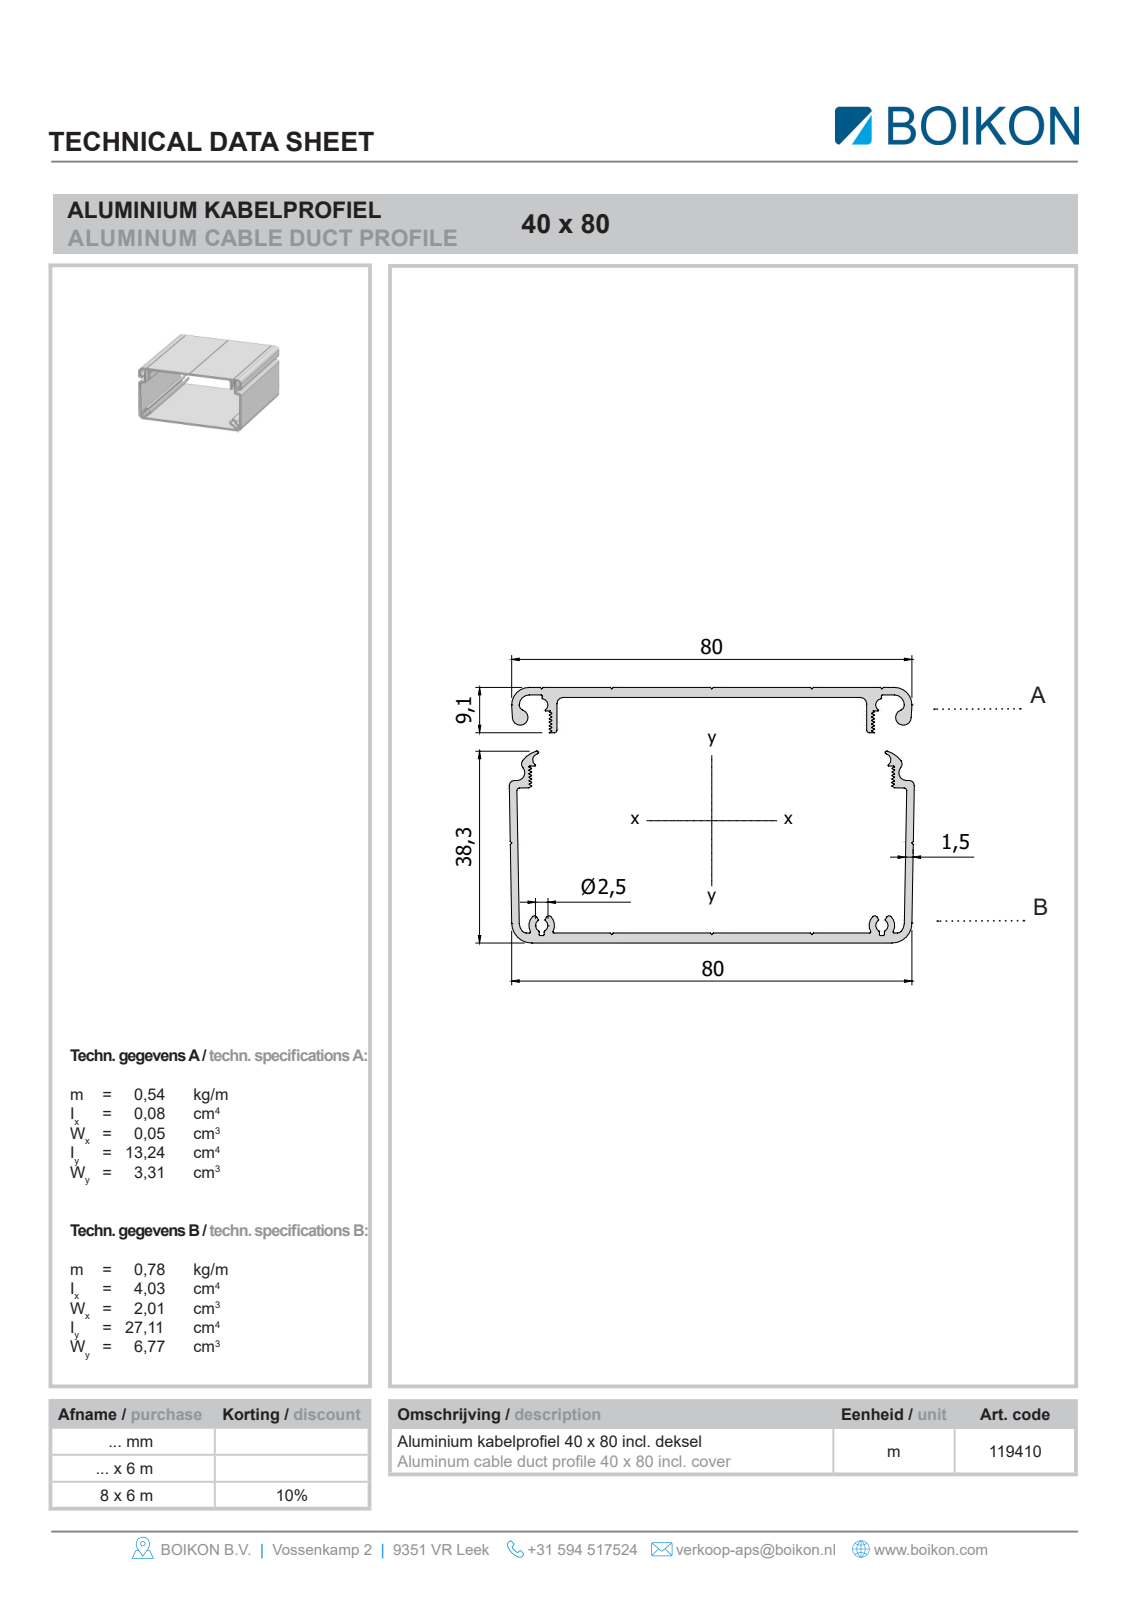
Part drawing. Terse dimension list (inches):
name: Root; 119410Kabelgootprofiel 40x80BOIKON0
written by: HiCAD 2013 1802.4 Build 509 (AUTOMOTIVE_DESIGN)
unit: in
bodies: 2 solids, 162 faces (85 planar, 77 cylindrical, 0 other)
size: 39.37 × 3.15 × 1.575
volume: 26.77 in³; area: 910 in²
rounds: 22× R0.02, 12× R0.012, 11× R0.005, 6× R0.059, 6× R0.079, 4× R0.118, 4× R0.138, 2× R0.01
face distances: 0.059, 1.516, 1.575, 1.457, 3.091, 3.15, 0.157, 2.933, 3.031, 0.28
